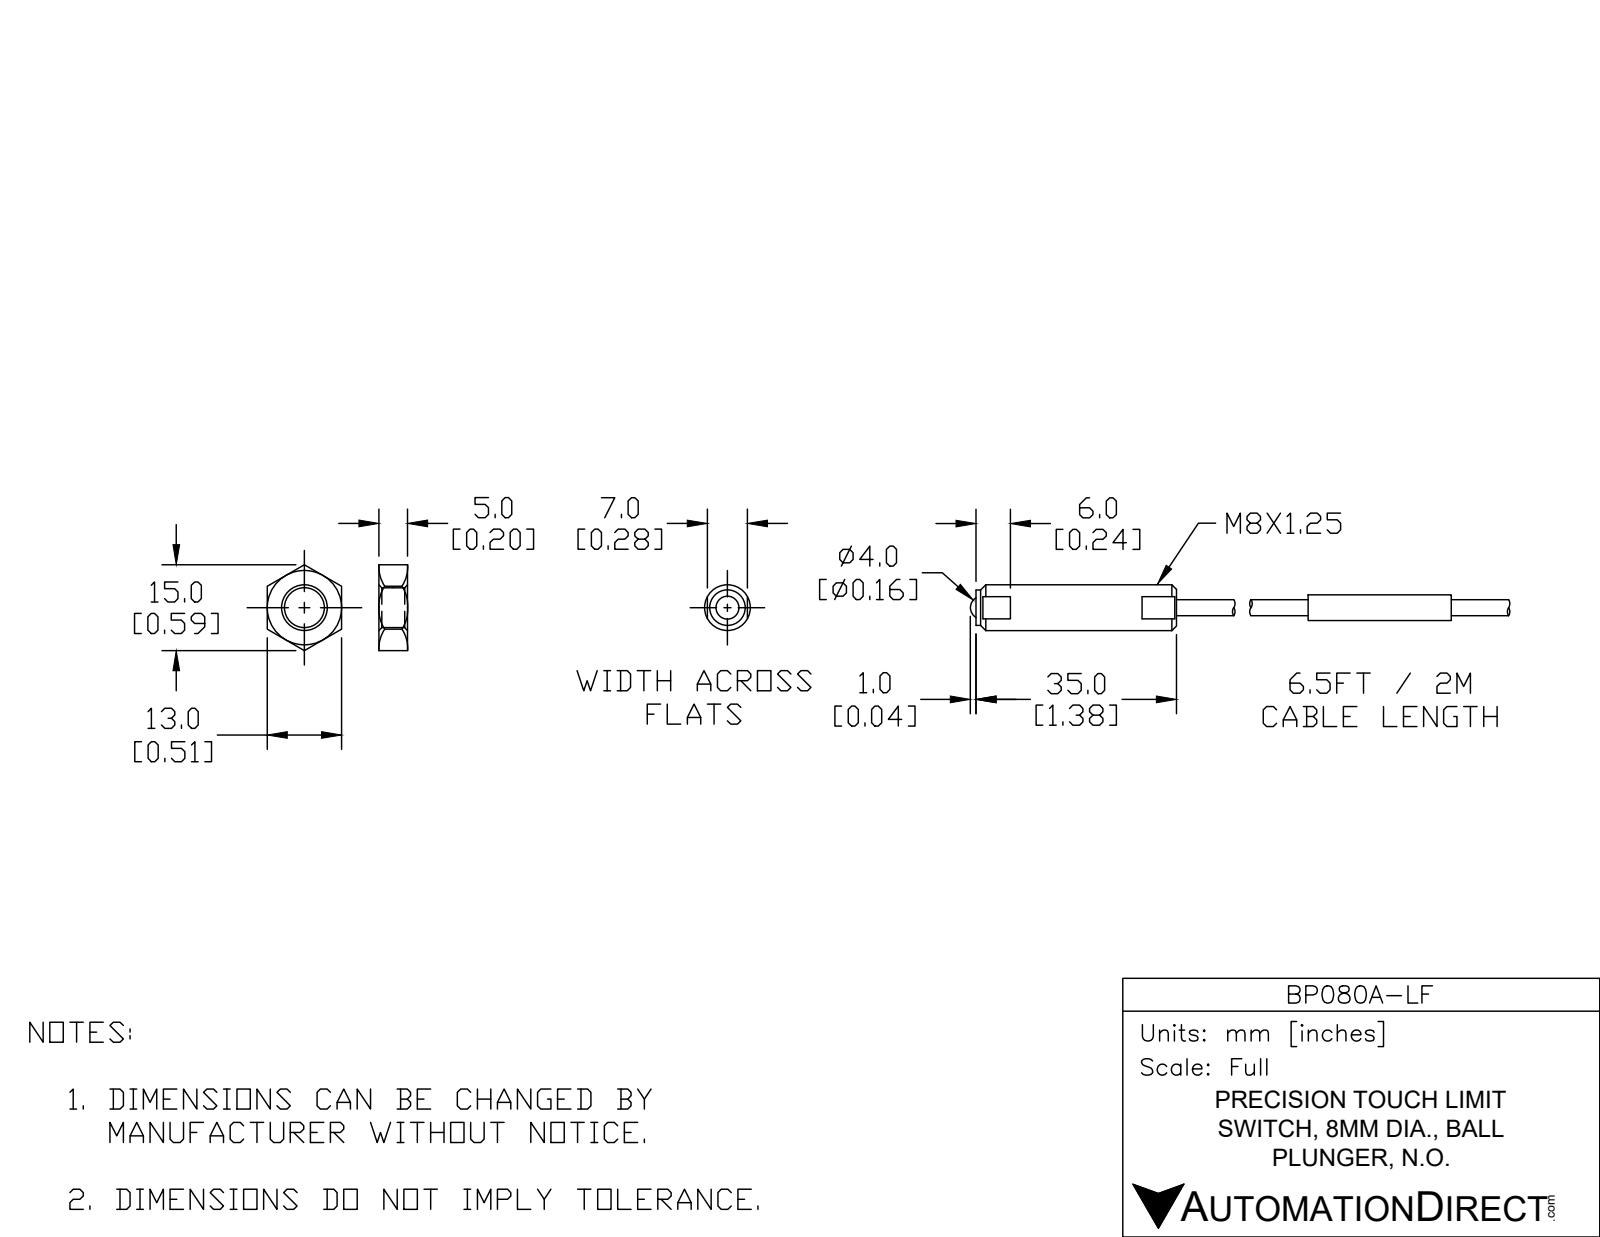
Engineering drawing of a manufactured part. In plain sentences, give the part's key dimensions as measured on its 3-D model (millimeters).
The part is named "BP080A-LF". Its 3-D file was written by "SolidWorks 2017 (CONFIG_CONTROL_DESIGN)". It is 2 solids with 101 faces: 28 planar, 63 cylindrical and 10 other. Overall it measures 94 by 8 by 8 millimeters. Its volume is 2 013 cubic millimeters and its surface area 2 019 square millimeters. Round bosses or shafts: 1 of diameter 8, 1 of diameter 6.2, 1 of diameter 4.5, 1 of diameter 2.8. The main face-to-face distances are 35, 58, 7, 46, 47, 11, 12, 23, 83, 48.
